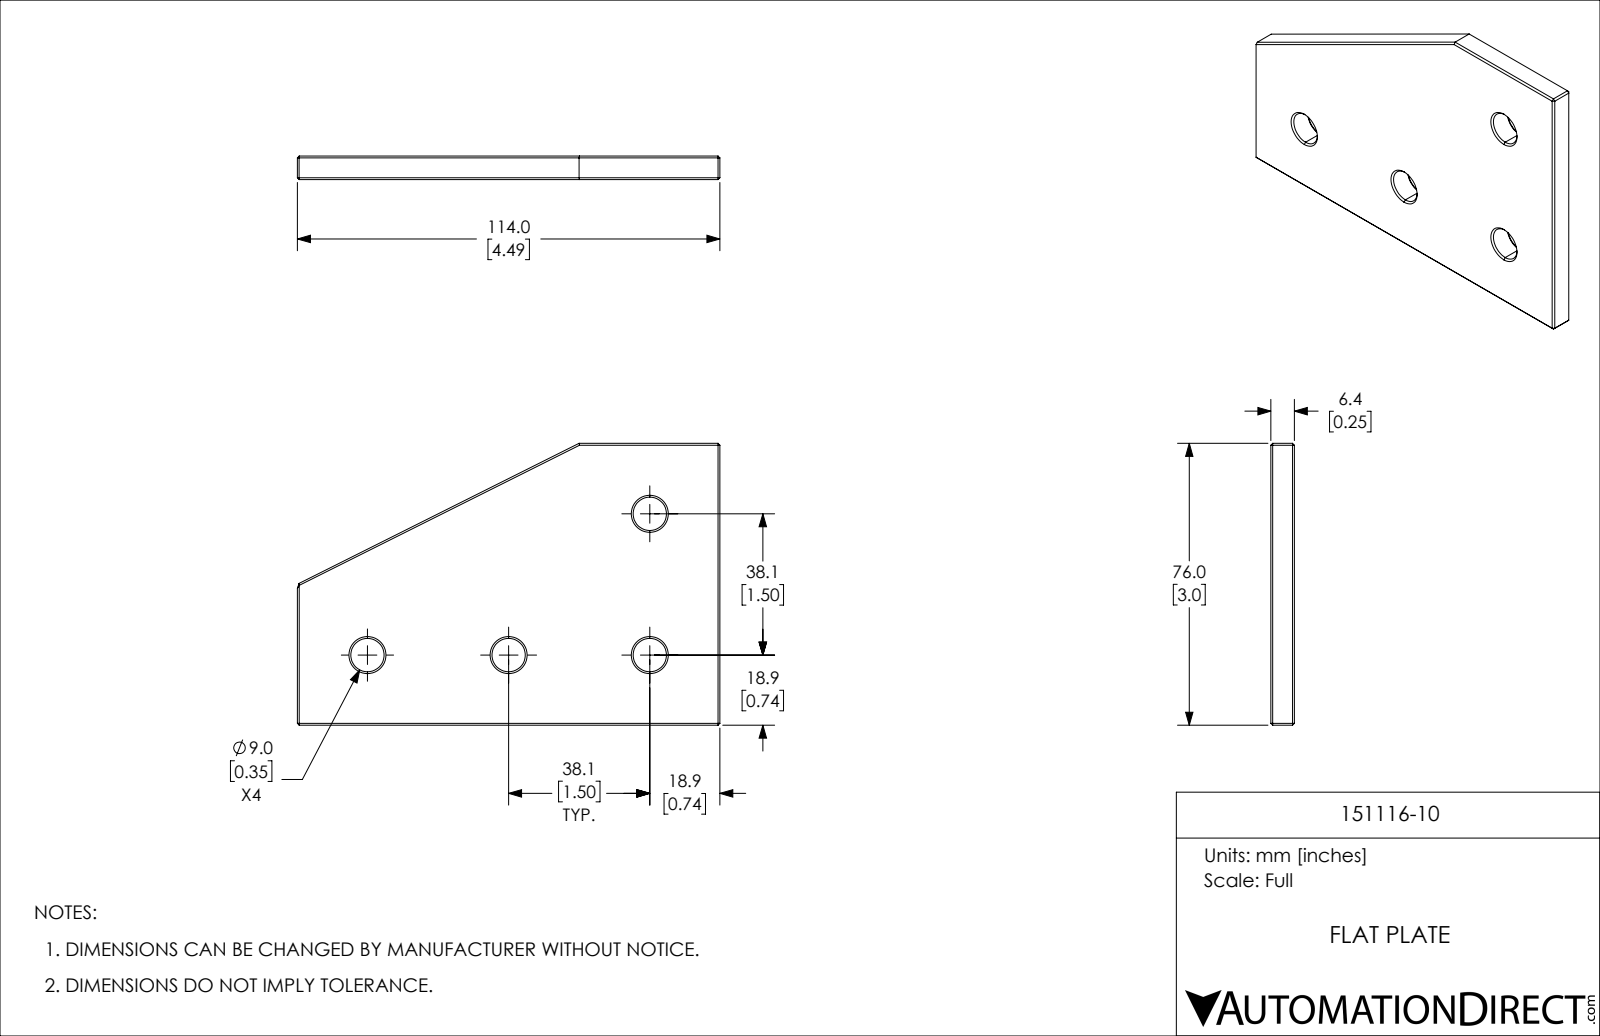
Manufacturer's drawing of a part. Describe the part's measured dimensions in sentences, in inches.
The part is named "151116-10". Its 3-D file was written by "SolidWorks 2024 (CONFIG_CONTROL_DESIGN)". It is 1 solid with 53 faces: 29 planar, 8 cylindrical and 16 other. Overall it measures 4.488 by 2.992 by 0.25 inches. Its volume is 2.692 cubic inches and its surface area 25.73 square inches. Round holes: 4 of diameter 0.354. The main face-to-face distances are 0.25, 2.992, 4.488, 2.265, 3.322, 5.261, 4.415, 4.415. The hole center spacings are 1.5, 2.121, 3, 3.354.
